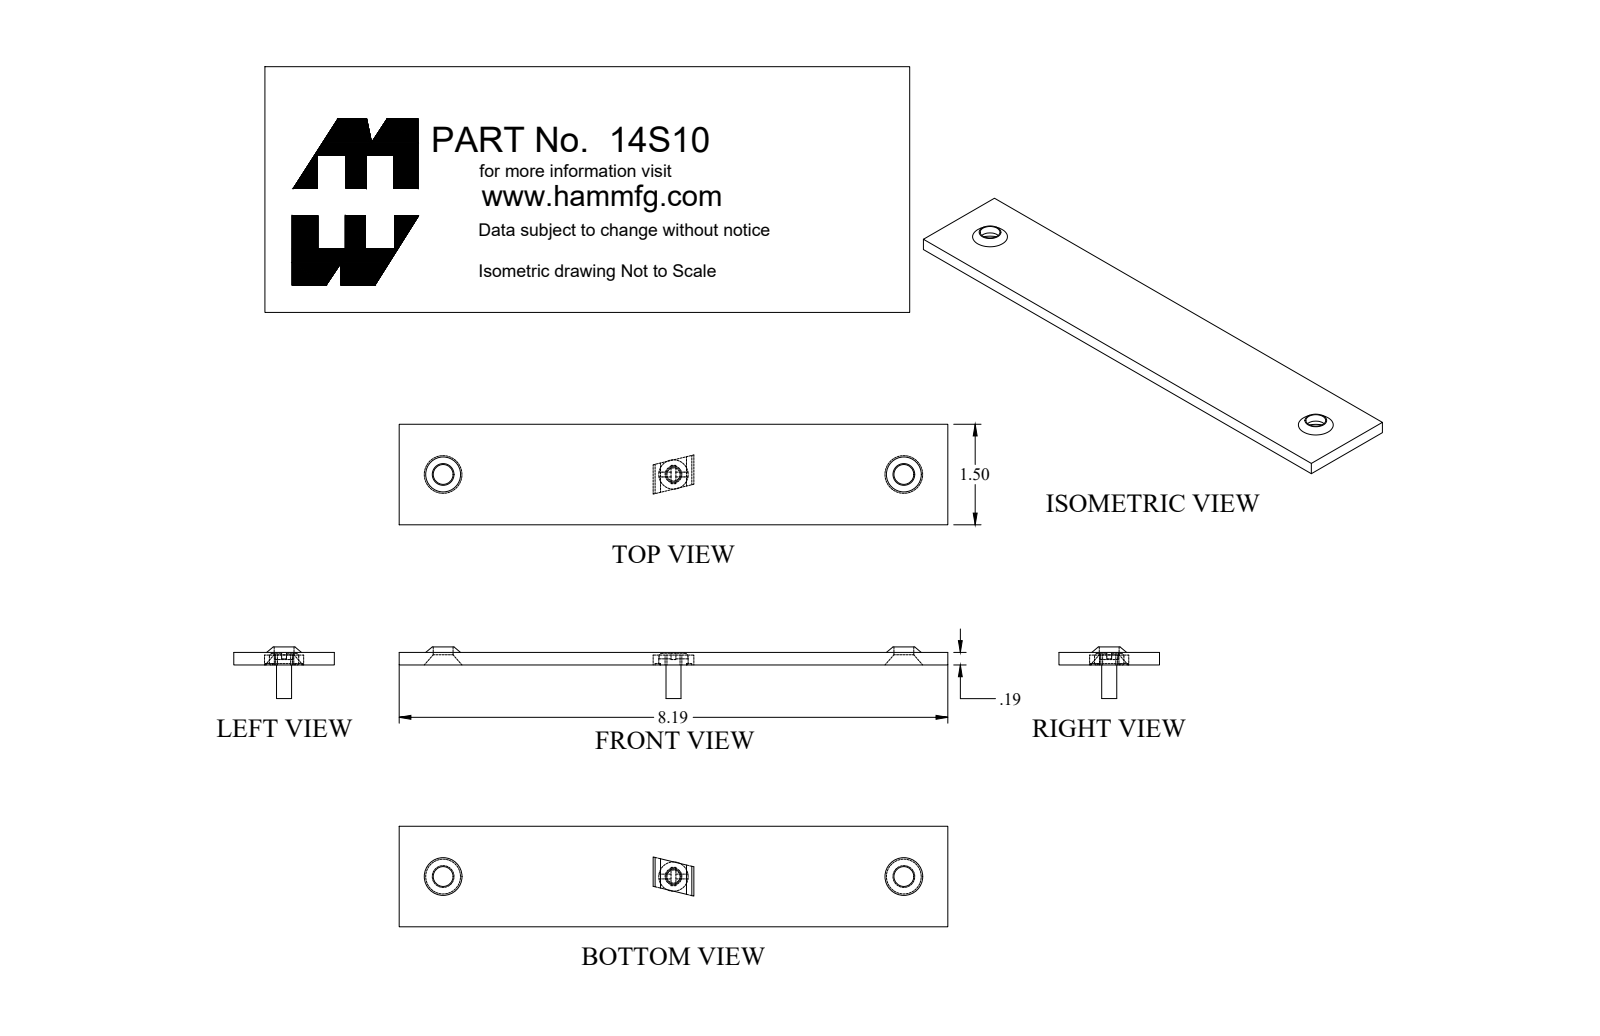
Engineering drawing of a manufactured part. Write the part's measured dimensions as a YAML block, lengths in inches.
part_name: "14S10"
step_written_by: "SolidWorks 2018 (AUTOMOTIVE_DESIGN)"
units: inches
bodies: {solids: 1, faces: 14, planar: 8, cylindrical: 2, other: 4}
overall_size: [8.187, 1.5, 0.27]
volume: 2.27
surface_area: 28.41
round_holes:
  - {diameter: 0.296, count: 2}
face_to_face_distances: [0.188, 1.5, 8.187, 0.27, 0.082]
hole_center_spacings: [6.875]
